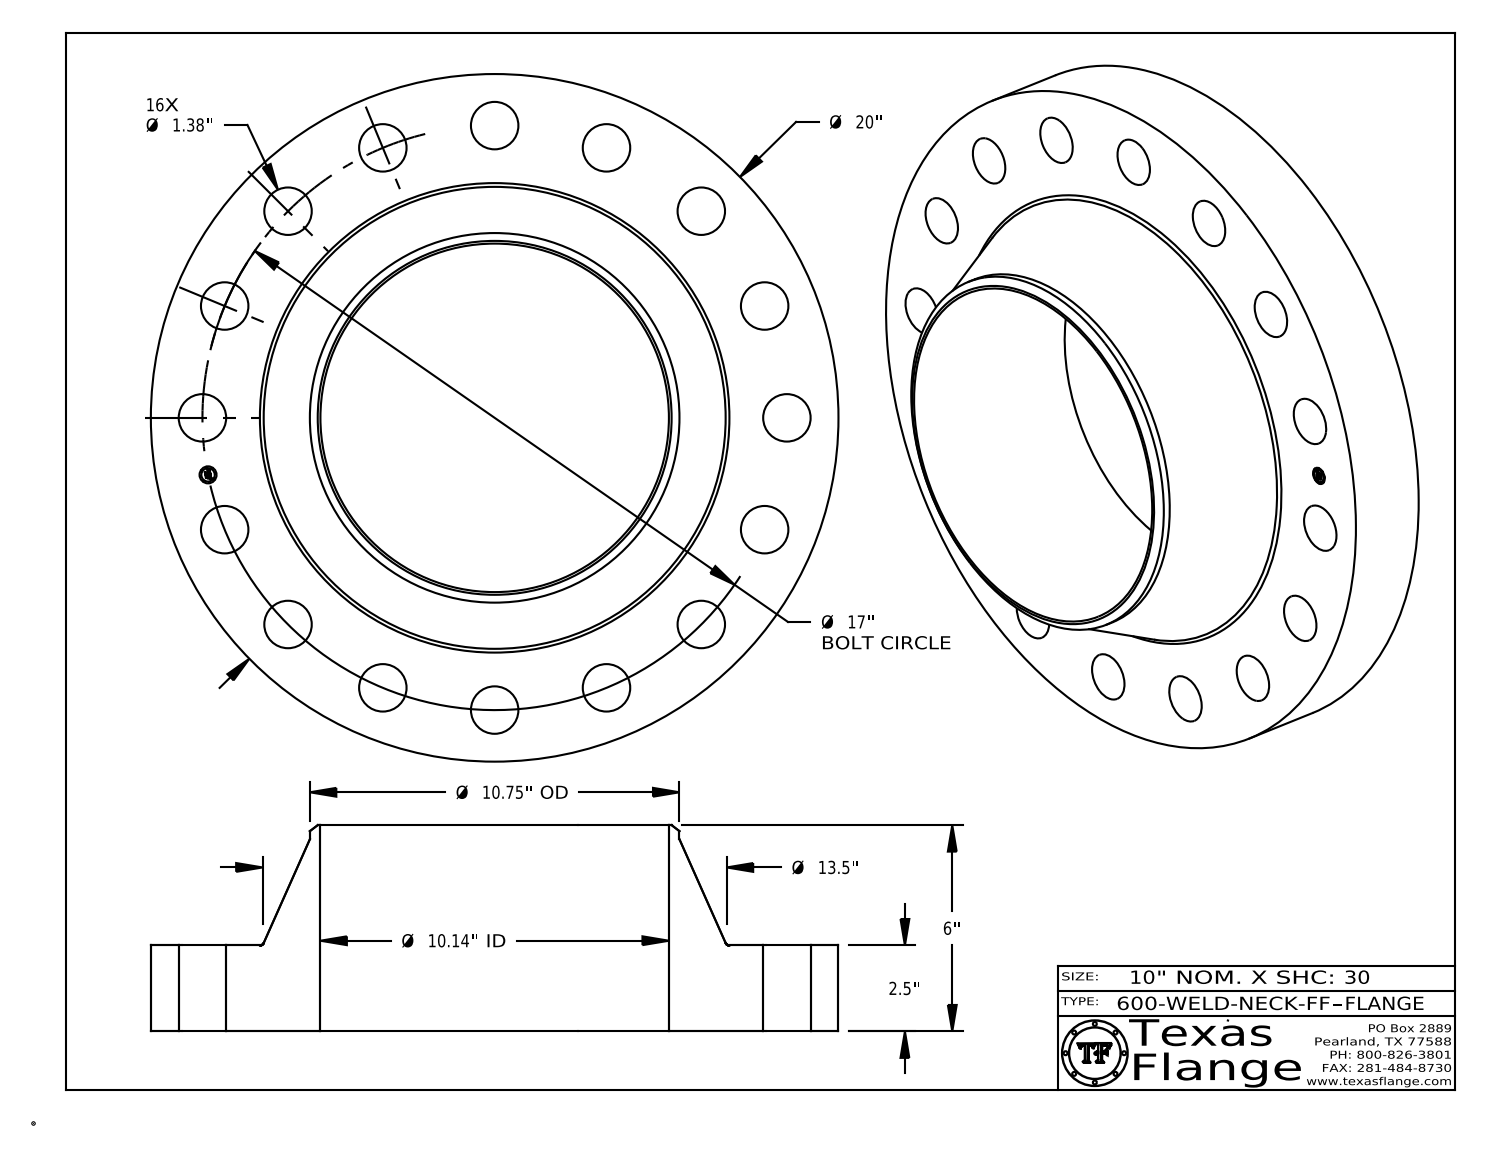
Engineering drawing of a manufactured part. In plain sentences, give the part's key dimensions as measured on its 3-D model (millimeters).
The part is named "600-WELD-NECK-FF". Its 3-D file was written by "CATIA V5 STEP AP214 (AUTOMOTIVE_DESIGN)". It is 1 solid with 432 faces: 368 planar, 58 cylindrical and 6 other. Overall it measures 508 by 508 by 152.4 millimeters. Its volume is 10 430 000 cubic millimeters and its surface area 661 900 square millimeters. Round holes: 16 of diameter 35.1, 1 of diameter 12.6, 1 of diameter 257.5. Round bosses or shafts: 8 of diameter 0.8, 1 of diameter 508, 1 of diameter 273.1, 1 of diameter 9.9. The main face-to-face distances are 63.5, 152.4, 88.9, 63.1, 0.4, 89.3, 3.8, 3.7, 0.7, 2.4. The hole center spacings are 84.3, 359, 215.9, 165.3, 305.3, 239.9, 239.9, 398.9.
